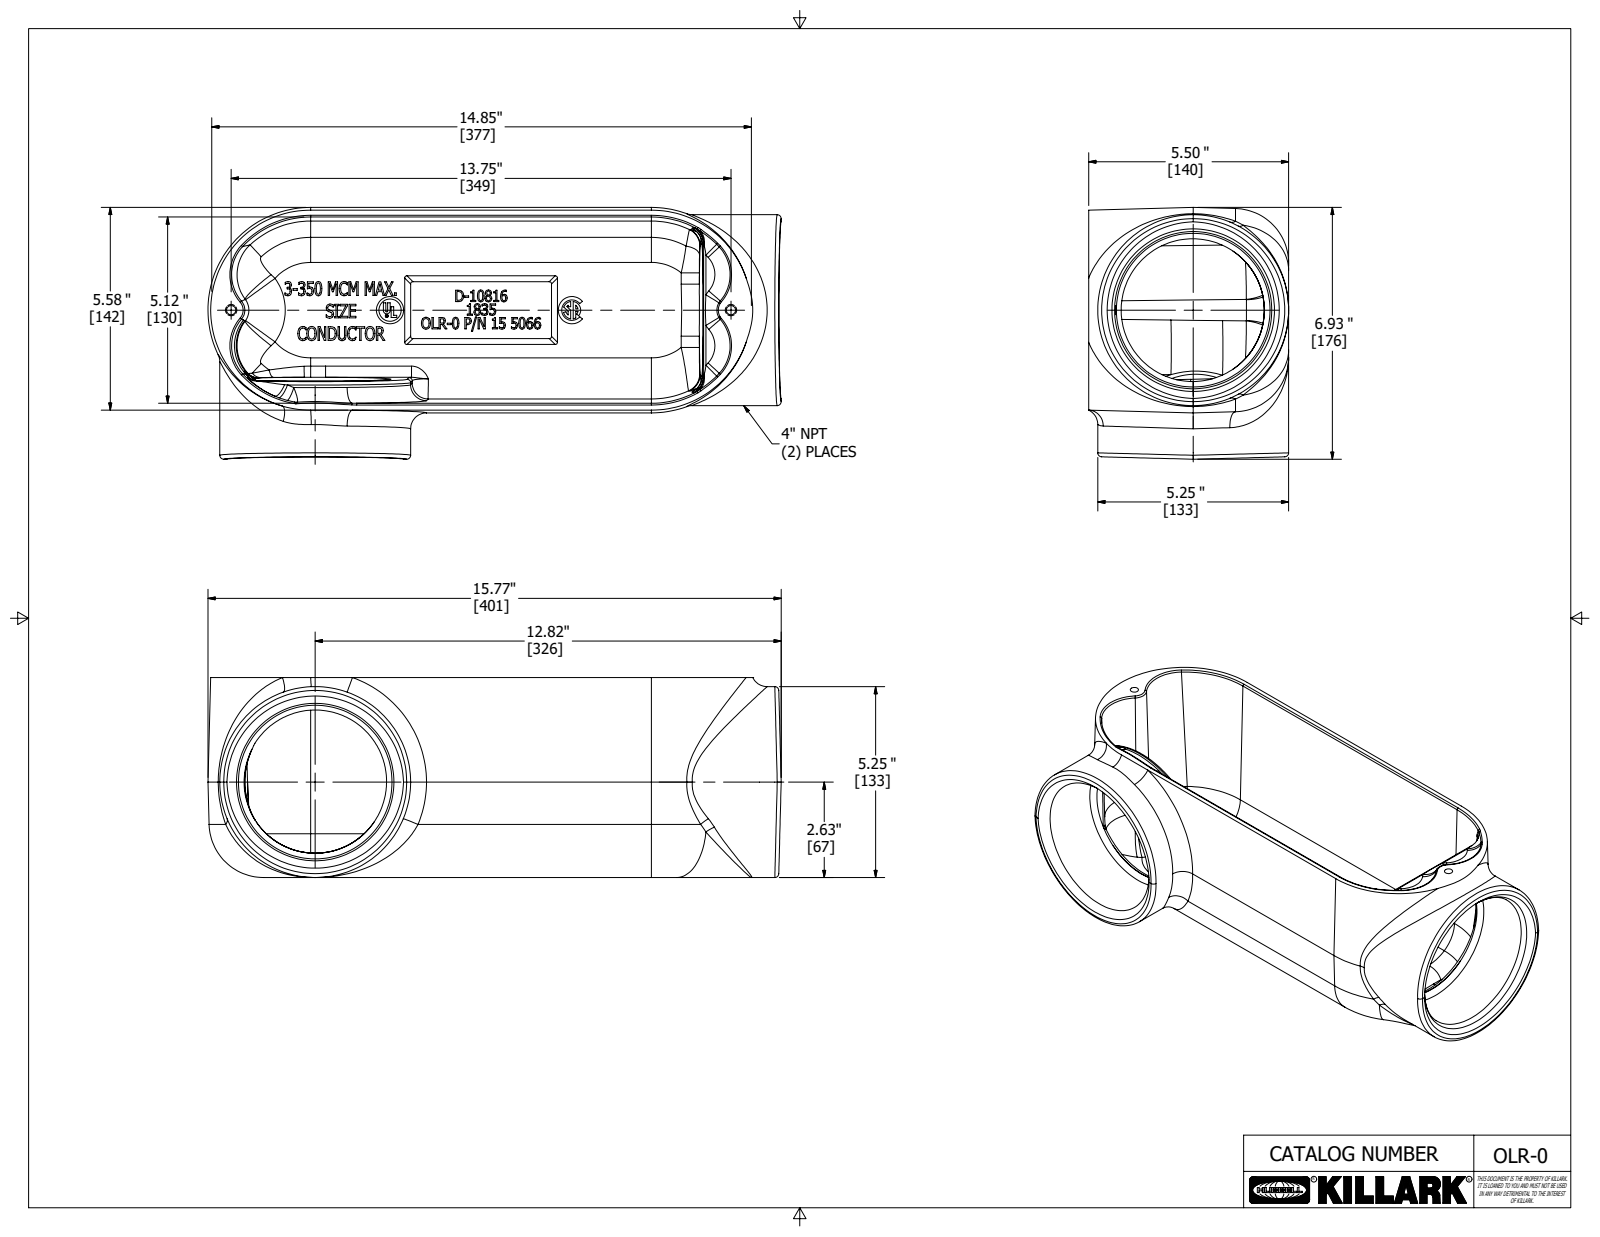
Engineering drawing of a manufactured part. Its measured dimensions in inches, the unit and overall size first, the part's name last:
Units: inches
Overall size (bounding box): 15.769 × 6.925 × 5.632
Round holes (diameter × count): ⌀0.252 ×2, ⌀0.07 ×1, ⌀0.611 ×1
Round bosses / shafts (diameter × count): ⌀5.25 ×2, ⌀0.75 ×1, ⌀0.083 ×1
Partial cylindrical surfaces — rounded edges, fillets, slot ends (radius × count): R0.031 ×4, R0.125 ×4, R0.047 ×2, R0.375 ×2, R1.25 ×2, R1.5 ×2, R0.008 ×1, R0.013 ×1
Main face-to-face distances: 5.313, 0.187, 0.337, 5.65, 5.5, 5.313, 0.094, 0.281, 5.219, 0.025
Hole centre spacings: 0.183, 4.284, 4.371, 9.379, 9.47, 13.75
Volume: 89.13 in³ · Surface area: 540 in²
Bodies: 1 solid, 1309 faces (656 planar, 45 cylindrical, 608 other)
Part name (STEP PRODUCT): 10816-3
STEP written by: Autodesk Inventor 2018 (AUTOMOTIVE_DESIGN)
